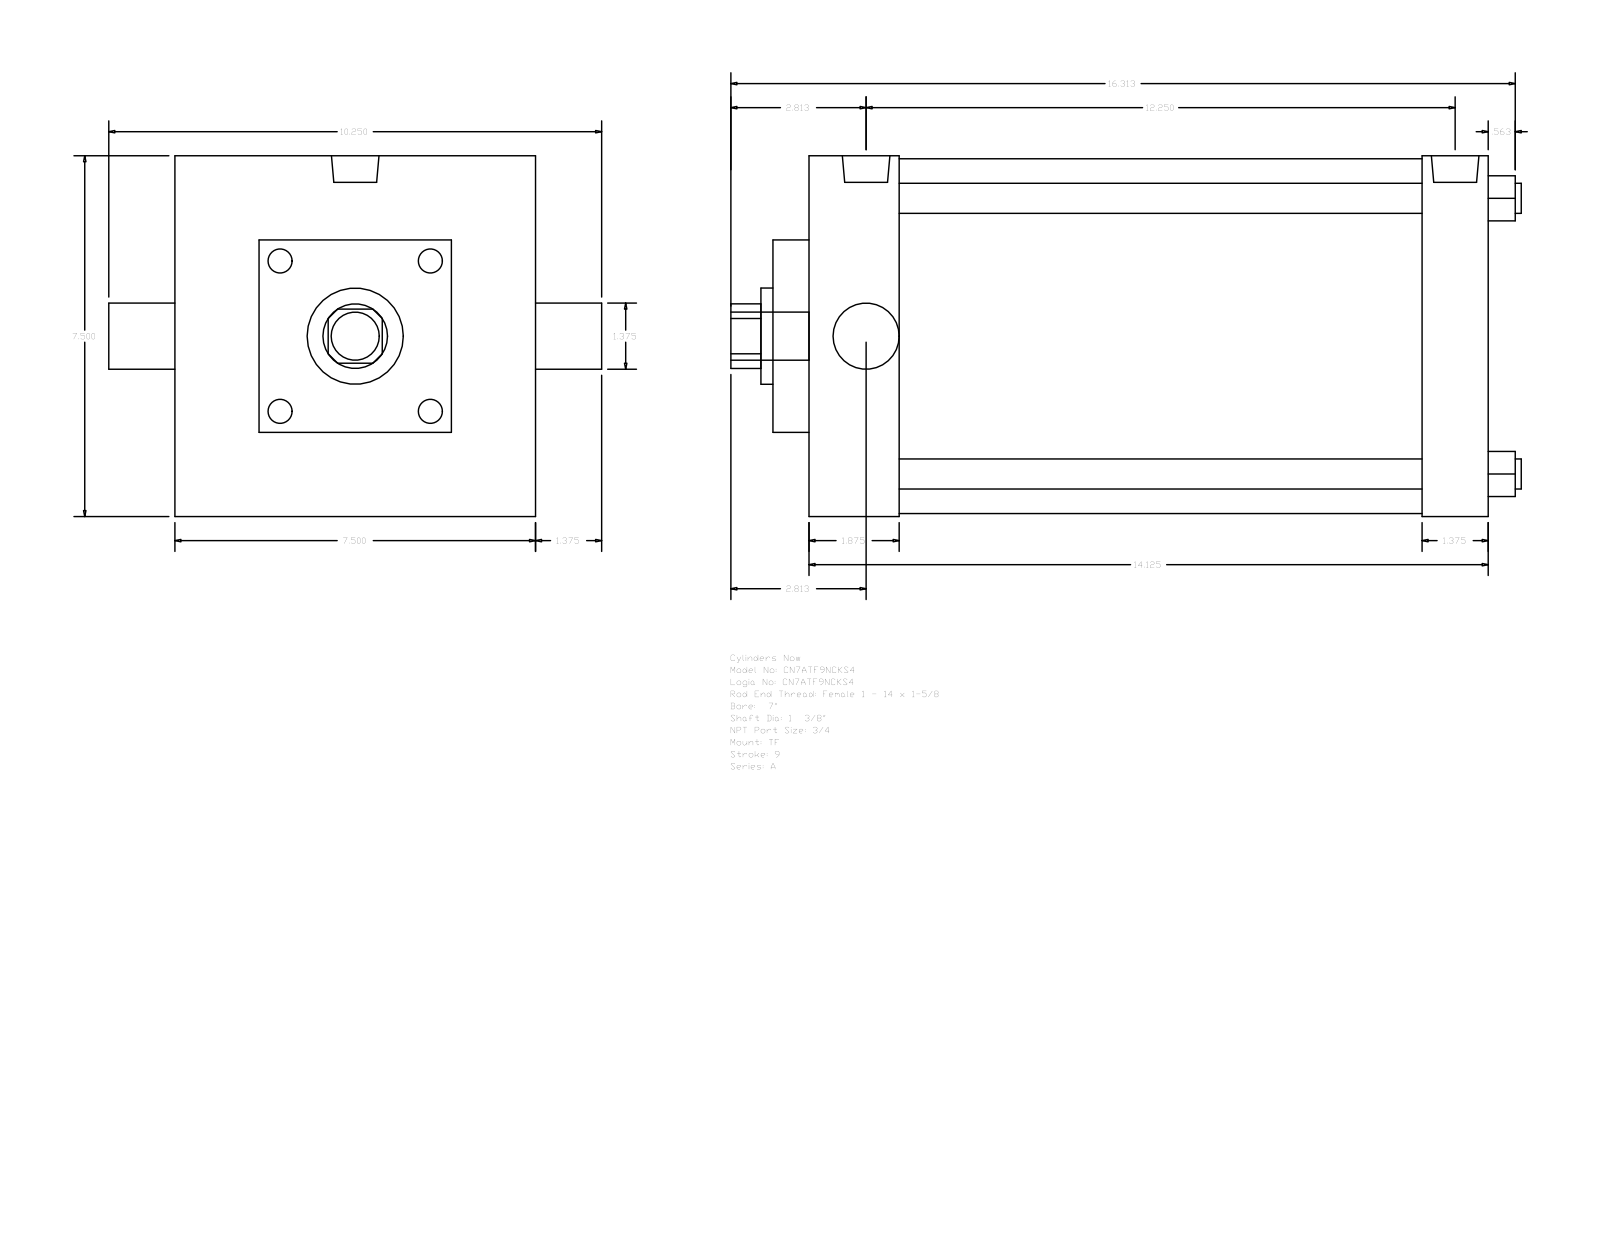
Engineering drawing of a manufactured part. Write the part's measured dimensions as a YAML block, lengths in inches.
part_name: "A_TF__0700_1.375"
step_written_by: "GSSL Pune (CONFIG_CONTROL_DESIGN)"
units: inches
bodies: {solids: 0, faces: 89, planar: 65, cylindrical: 24, other: 0}
overall_size: [16.437, 10.25, 7.5]
round_holes:
  - {diameter: 0.625, count: 4}
  - {diameter: 1.375, count: 2}
  - {diameter: 2, count: 1}
  - {diameter: 7.375, count: 1}
round_bosses_or_shafts:
  - {diameter: 0.594, count: 3}
  - {diameter: 0.989, count: 2}
  - {diameter: 1, count: 1}
partial_cylinders:
  - {radius: 0.672, count: 1}
face_to_face_distances: [7.5, 14.125, 1.375, 0.75, 14.875, 2.625, 1.875, 12.25, 13.5, 12.75]
hole_center_spacings: [4.052, 5.73, 8.103]
